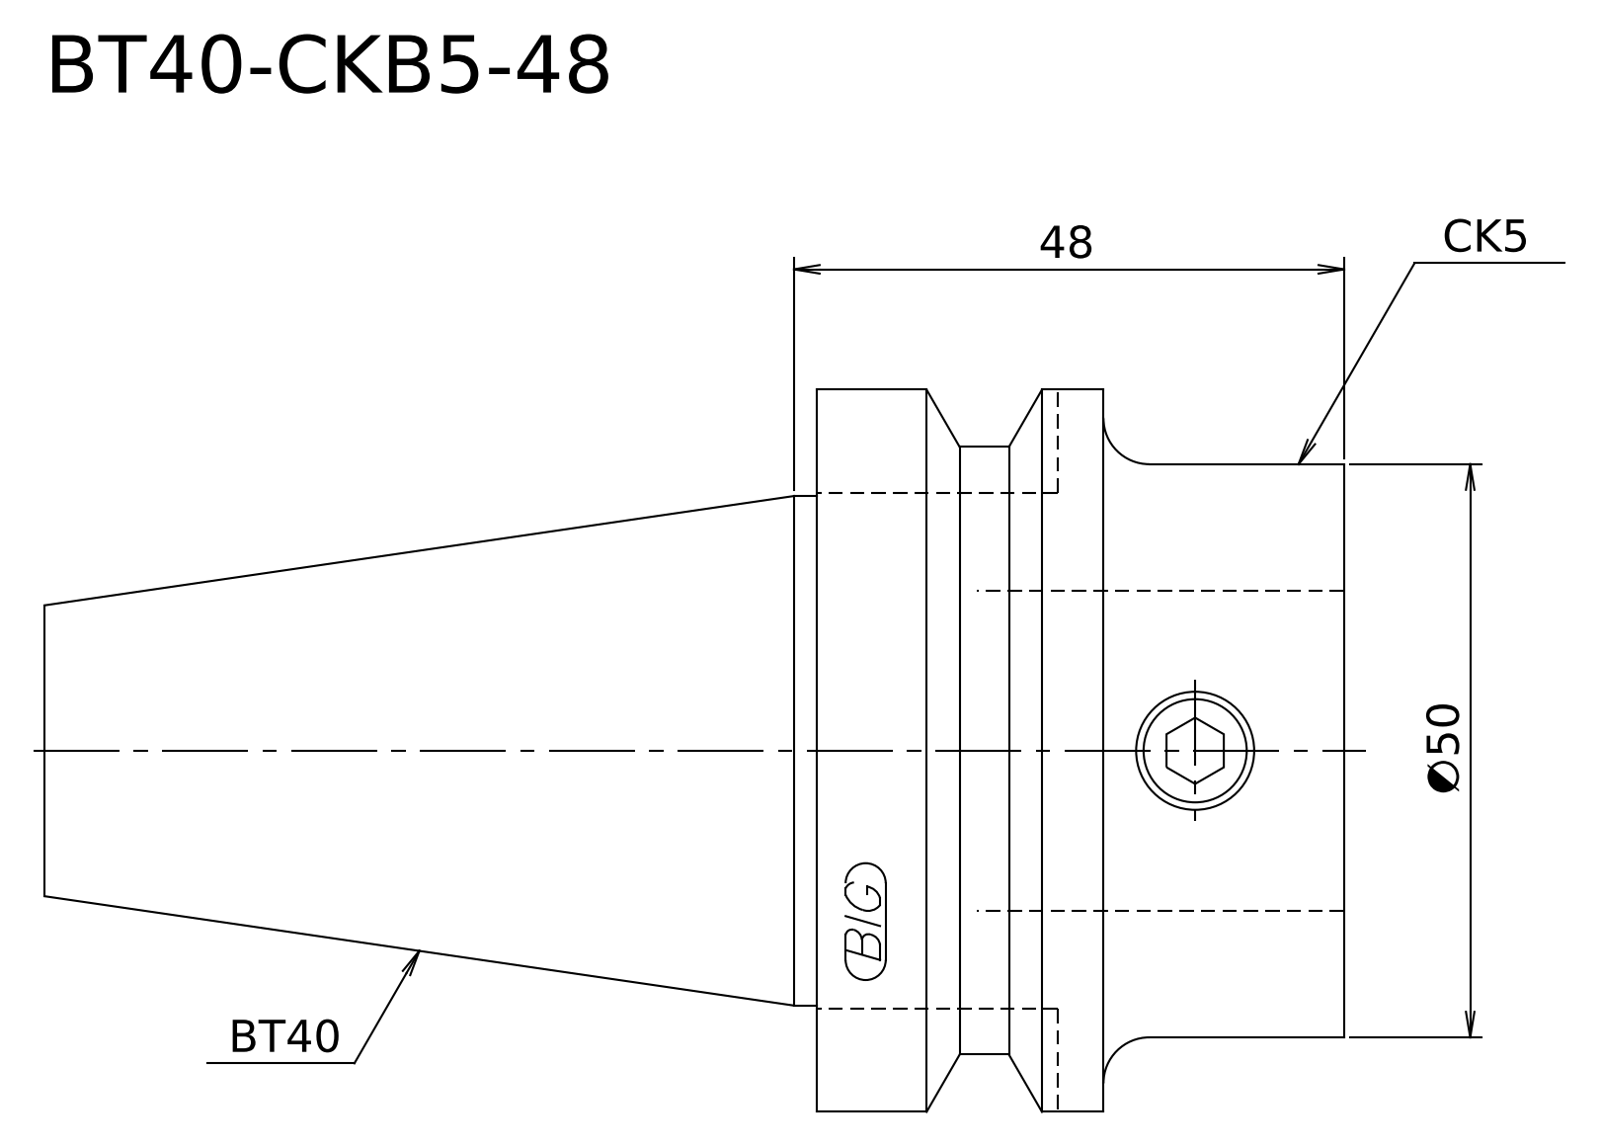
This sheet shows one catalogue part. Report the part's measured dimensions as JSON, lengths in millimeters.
{"step_written_by": "Kubotek KeyCreator V8.5.1 (14335) (CONFIG_CONTROL_DESIGN)", "units": "millimeters", "bodies": {"solids": 1, "faces": 14, "planar": 4, "cylindrical": 5, "other": 5}, "overall_size": [113.4, 63, 63], "volume_mm3": 181684, "surface_area_mm2": 21293, "round_bosses_or_shafts": [[63, 1], [53, 1], [50, 1], [44.45, 1]], "face_to_face_distances": [46, 113.4, 67.4, 21, 25, 92.4]}
